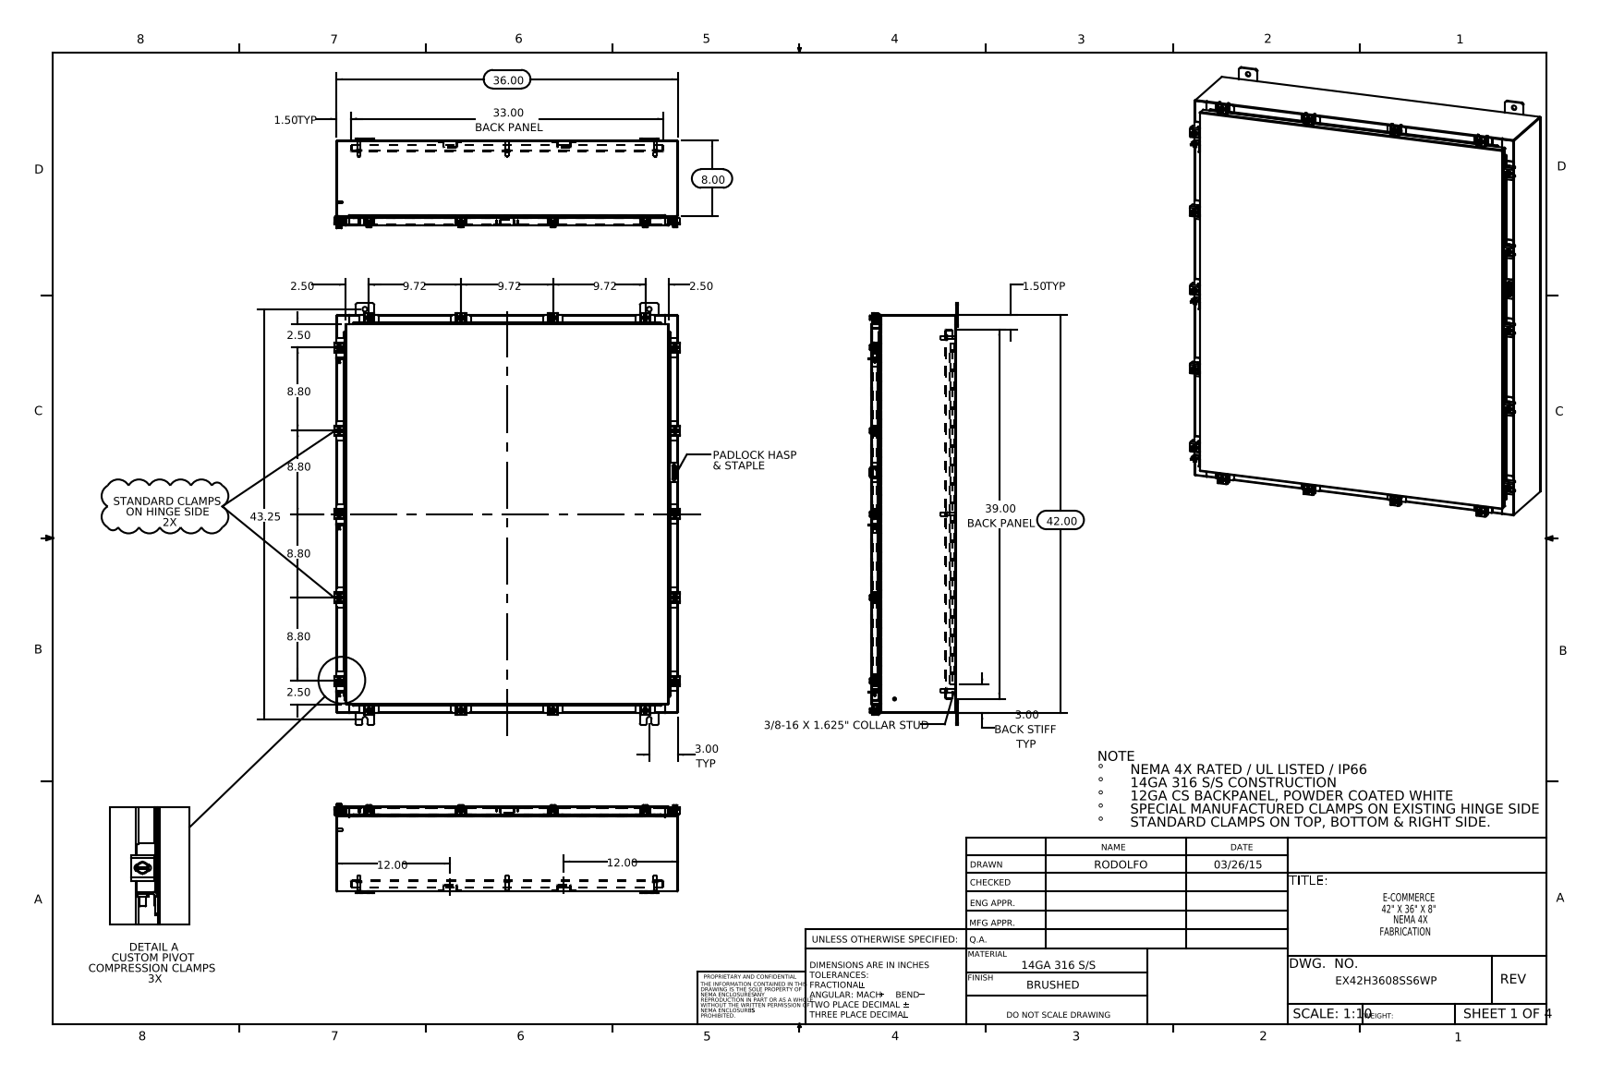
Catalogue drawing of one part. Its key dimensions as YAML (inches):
part_name: "EX42H3608SS6WP Door Stiffener; EX42H3608SS6WP Special Clamp; EX42H3608SS6WP Body; EX42H3608SS6WP Top (+8 more)"
step_written_by: "SolidWorks 2014 (CONFIG_CONTROL_DESIGN)"
units: inches
bodies: {solids: 126, faces: 3106, planar: 1613, cylindrical: 1195, other: 298}
overall_size: [44.5, 36.421, 9.453]
volume: 530.7
surface_area: 13133
round_holes:
  - {diameter: 0.213, count: 18}
  - {diameter: 0.26, count: 18}
  - {diameter: 0.5, count: 12}
  - {diameter: 0.25, count: 7}
  - {diameter: 0.125, count: 1}
round_bosses_or_shafts:
  - {diameter: 0.5, count: 18}
  - {diameter: 0.25, count: 18}
  - {diameter: 0.399, count: 15}
  - {diameter: 0.625, count: 8}
  - {diameter: 0.375, count: 8}
  - {diameter: 0.33, count: 8}
  - {diameter: 0.157, count: 6}
  - {diameter: 0.14, count: 6}
partial_cylinders:
  - {radius: 0.06, count: 76}
  - {radius: 0.013, count: 38}
  - {radius: 0.141, count: 36}
  - {radius: 0.088, count: 34}
  - {radius: 0.12, count: 33}
  - {radius: 0.09, count: 27}
  - {radius: 0.05, count: 25}
  - {radius: 0.145, count: 24}
face_to_face_distances: [0.075, 8.9, 8.826, 8.975, 0.104, 1, 1.075, 7.826, 7.9, 1.179]
hole_center_spacings: [1.969, 2.347, 4.44, 13.972, 14.729, 16.126, 16.624, 17]
